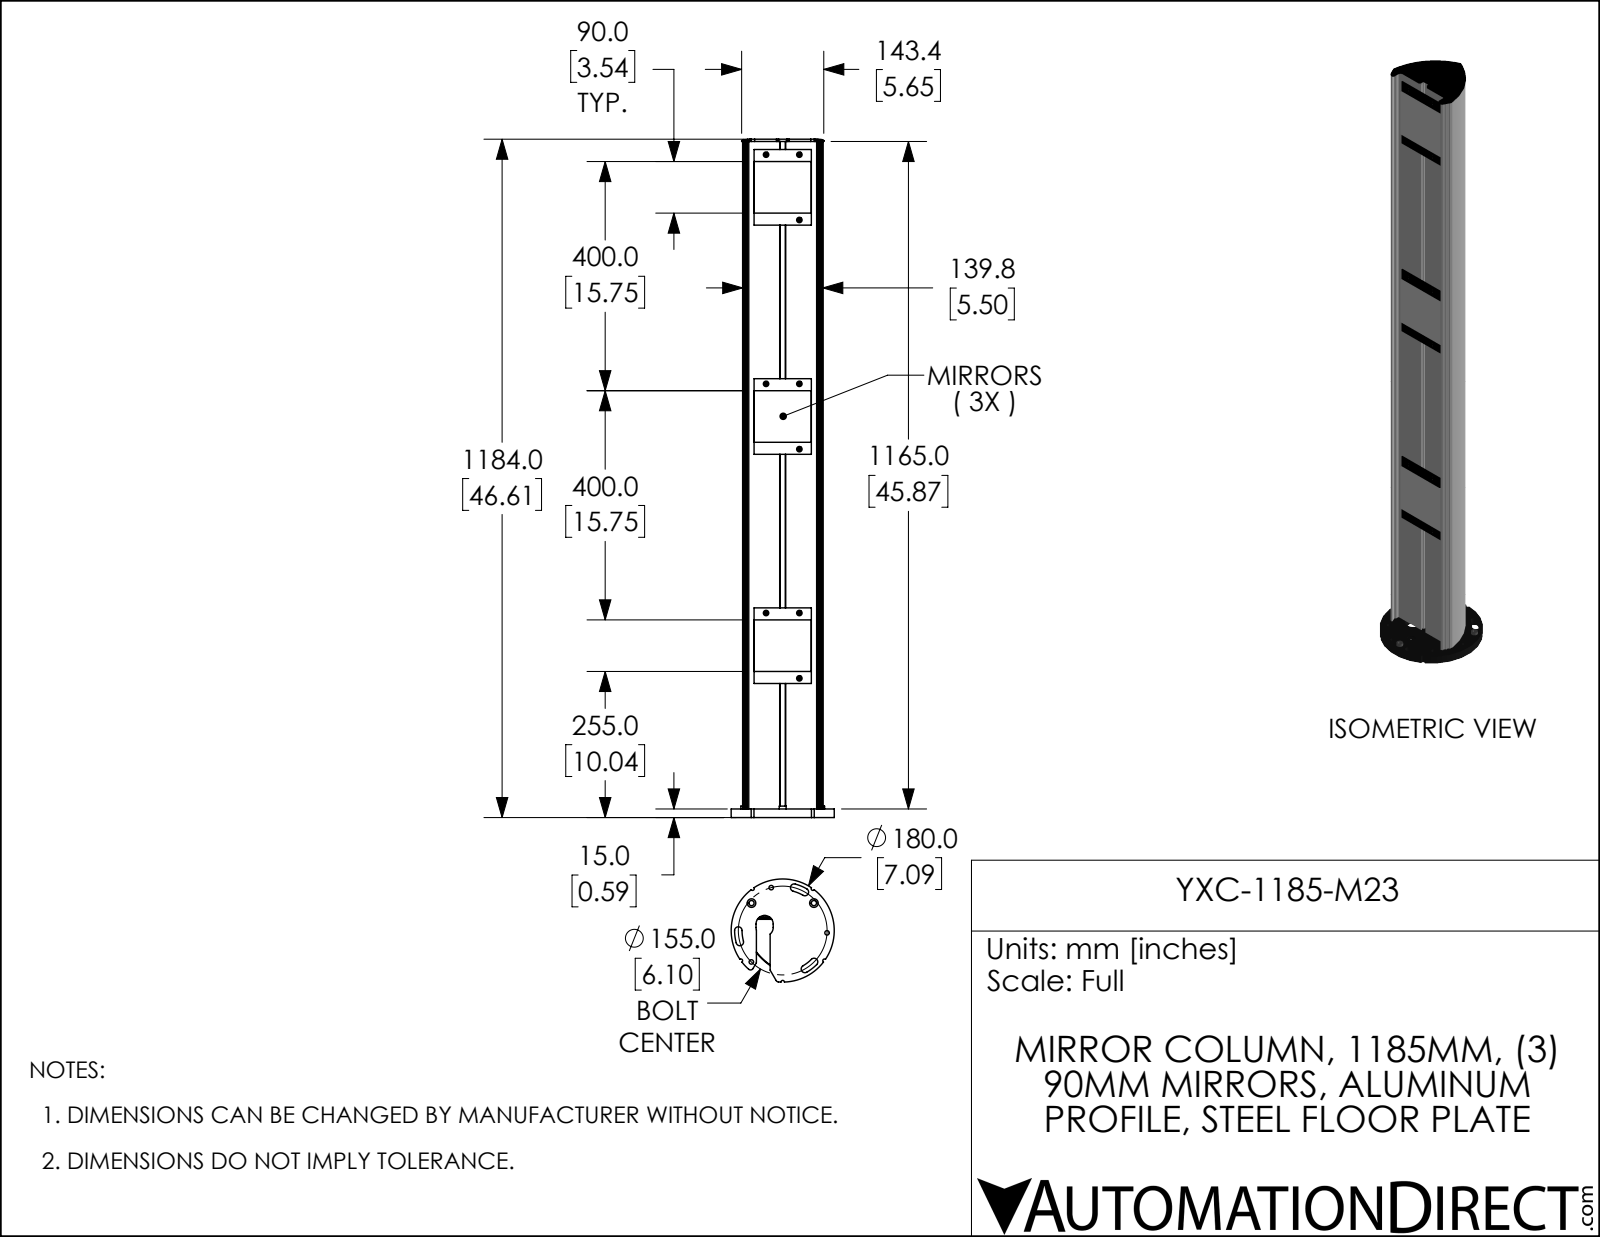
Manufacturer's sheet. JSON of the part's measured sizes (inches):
{"part_name": "YXC_1185_M23", "step_written_by": "Creo Elements/Direct Modeling 18.1B 29-Sep-2012 (C) Parametric Technology GmbH (AUTOMOTIVE_DESIGN)", "units": "inches", "bodies": {"solids": 1, "faces": 392, "planar": 250, "cylindrical": 110, "other": 32}, "overall_size": [46.614, 7.087, 7.085], "volume_in3": 666.4, "surface_area_in2": 1100, "round_holes": [[0.307, 3], [0.591, 3], [0.354, 2], [0.173, 1]], "round_bosses_or_shafts": [[0.236, 9], [0.472, 3], [7.087, 1]], "partial_cylinders_radius": [[0.118, 9], [0.256, 6], [0.236, 5], [0.052, 4], [4.685, 4], [0.197, 3], [0.039, 2], [0.052, 2]], "face_to_face_distances": [0.059, 0.118, 0.197, 0.256, 0.591, 0.138, 0.079, 0.394, 0.472, 0.335], "hole_center_spacings": [2.146, 1.255, 1.257, 1.722, 2.235, 3.121, 3.717, 3.719]}
